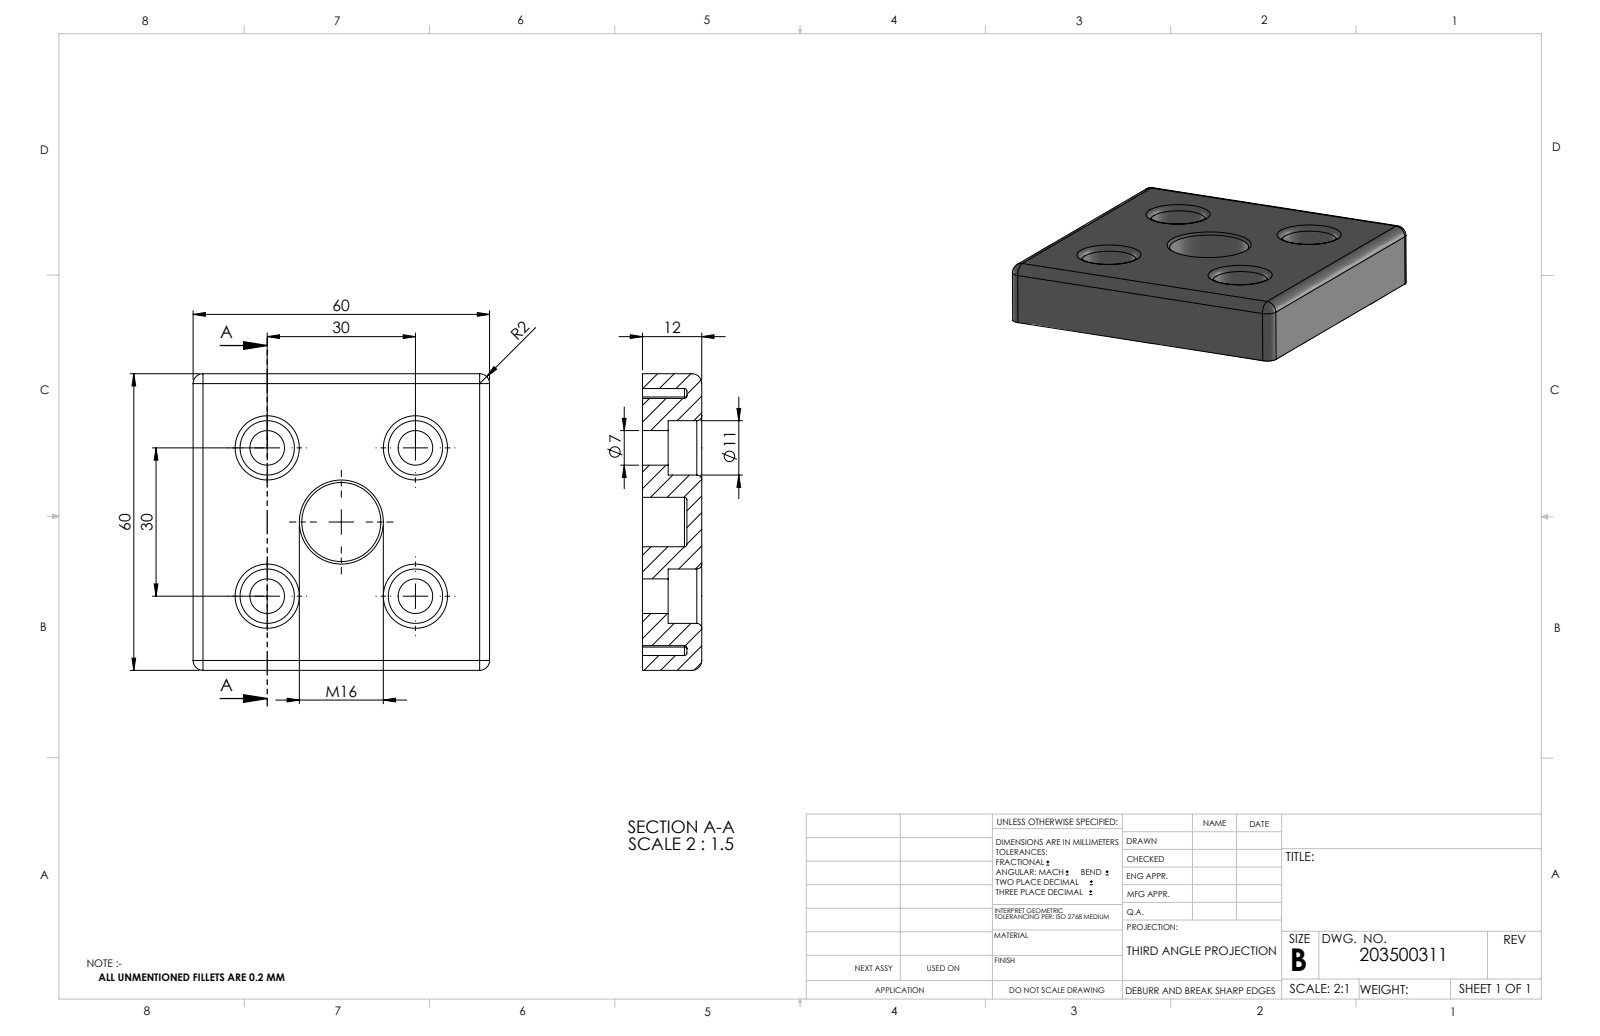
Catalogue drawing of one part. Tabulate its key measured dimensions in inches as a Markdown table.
| quantity | value |
| --- | --- |
| part name | 203500311_c_1 |
| STEP written by | SolidWorks 2014 (CONFIG_CONTROL_DESIGN) |
| units | inches |
| bodies | 1 solid, 171 faces (26 planar, 87 cylindrical, 58 other) |
| overall size | 2.362 × 2.362 × 0.472 |
| volume | 1.639 in³ |
| surface area | 23.52 in² |
| round holes (diameter × count) | 0.276 × 4, 0.433 × 4, 0.63 × 1 |
| round bosses / shafts (diameter × count) | 0.787 × 4 |
| partial cylindrical surfaces (radius × count) | 0.02 × 17, 0.039 × 16, 0.079 × 8, 0.433 × 1 |
| main face-to-face distances | 0.118, 0.472, 2.244, 2.362, 0.354, 2.126, 0.205, 0.15, 0.268, 0.197 |
| hole center spacings | 0.835, 1.181, 1.67 |
